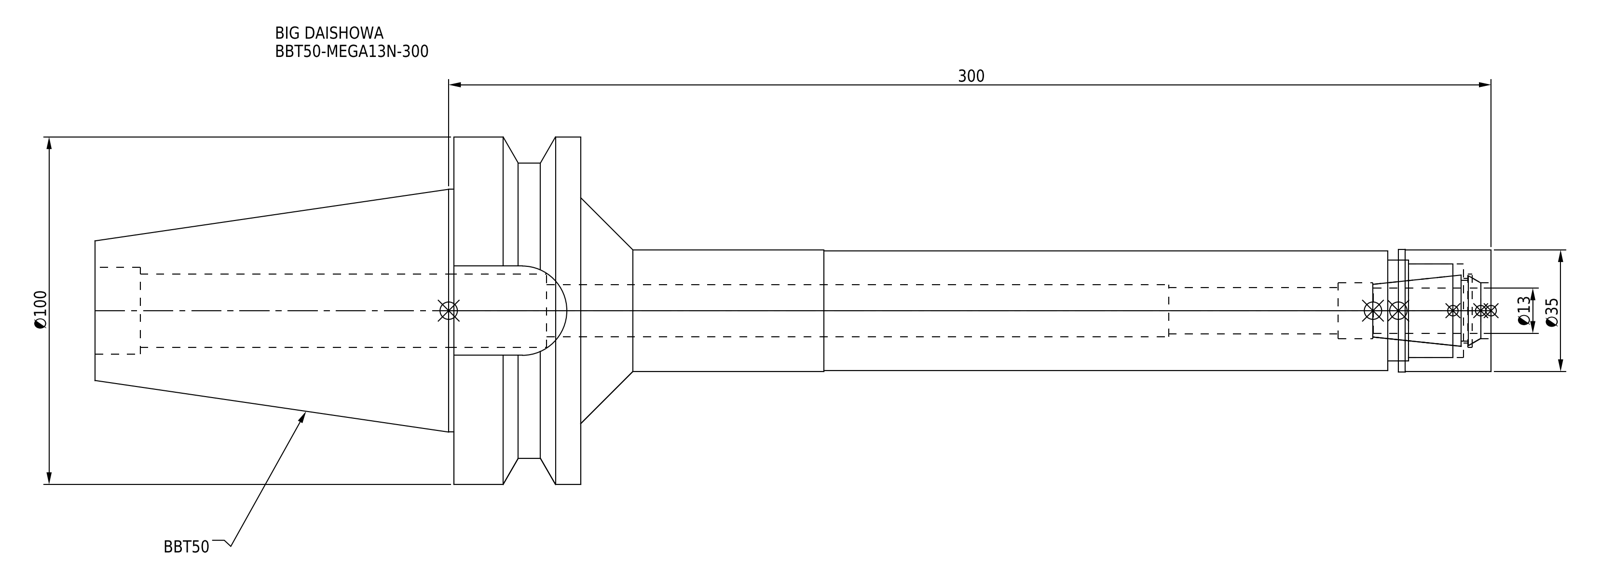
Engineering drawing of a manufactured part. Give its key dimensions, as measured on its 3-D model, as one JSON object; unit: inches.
{"part_name": "DXF_TEMP_ASSY_ASM_4_ASM.stp; BBT50-MEGA13N-300_1.stp; MGN13_1.stp; BBT50-MEGA13N-300 (+3 more)", "step_written_by": "SolidWorks 2019 (CONFIG_CONTROL_DESIGN)", "units": "inches", "bodies": {"solids": 2, "faces": 82, "planar": 24, "cylindrical": 44, "other": 14}, "overall_size": [15.819, 3.937, 3.937], "volume_in3": 40.53, "surface_area_in2": 153.3, "round_holes": [[0.524, 1], [0.591, 1], [0.63, 1], [0.728, 1], [0.827, 1], [0.835, 1], [0.984, 1], [1.063, 1], [1.142, 1]], "round_bosses_or_shafts": [[3.937, 1], [3.346, 1], [2.75, 1], [1.39, 1], [1.378, 1], [1.358, 1]], "partial_cylinders_radius": [[0.506, 1]], "face_to_face_distances": [1.437, 5.504, 4.067, 2.787, 10.315, 11.752, 15.819, 1.051, 10.701, 1.012]}
